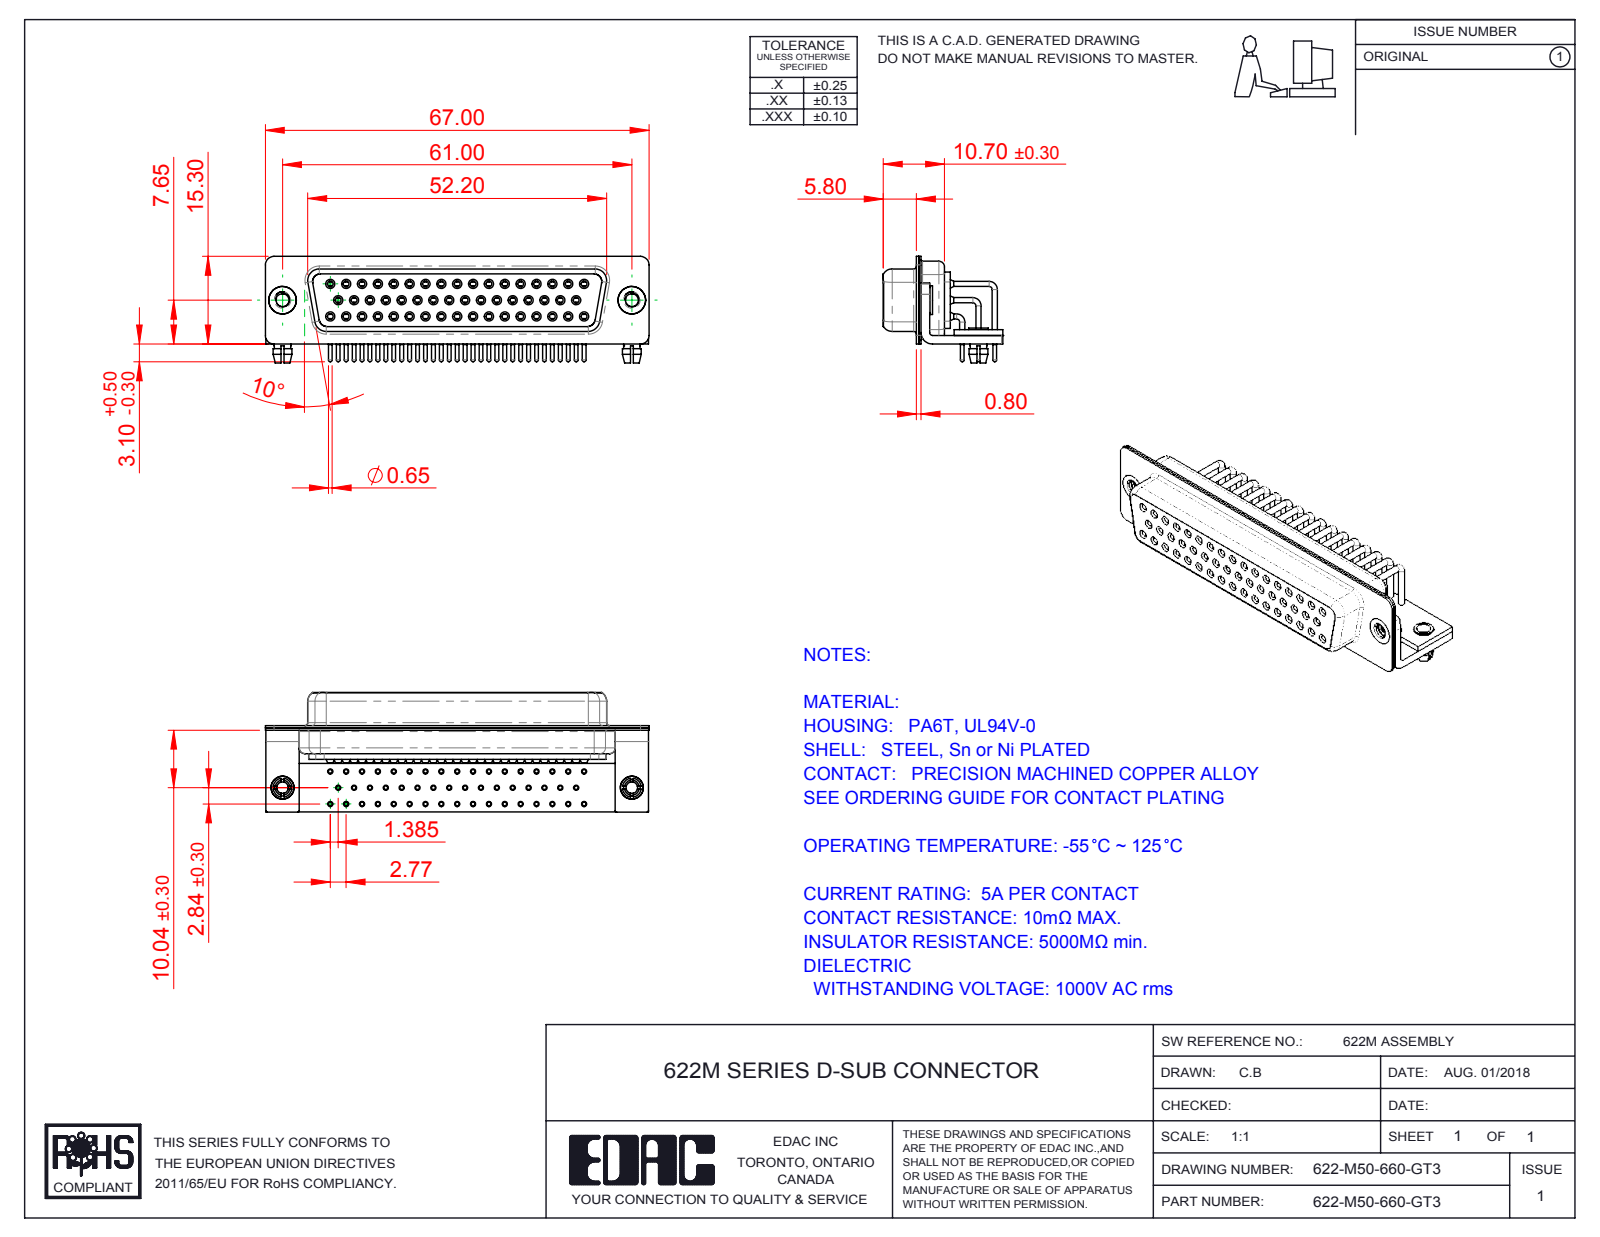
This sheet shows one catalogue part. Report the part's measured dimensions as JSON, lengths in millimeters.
{"part_name": "622M Stabilizer Bracket_50 Contacts; 622M Stabilizer Board_50 Contacts; 622-M50-660-GT3; 622M 4-40 Threaded Rivet_Stabilizer (+7 more)", "step_written_by": "SolidWorks 2016 (CONFIG_CONTROL_DESIGN)", "units": "millimeters", "bodies": {"solids": 60, "faces": 3171, "planar": 891, "cylindrical": 1441, "other": 839}, "overall_size": [67, 20.9, 18.6], "volume_mm3": 7790, "surface_area_mm2": 18357, "round_holes": [[2, 52], [0.9, 50], [1, 50], [1.1, 50], [1.7, 50], [1.8, 50], [2.26, 2], [2.5, 2], [3.2, 2], [4, 2], [4.8, 2]], "round_bosses_or_shafts": [[0.9, 59], [1.6, 50], [1.5, 50], [0.65, 50], [5, 2], [4.9, 2], [4, 2], [3.4, 2]], "partial_cylinders_radius": [[0.25, 16], [1.5, 16], [2, 13], [1.35, 8], [1.6, 8], [0.5, 5], [0.6, 4], [0.65, 4]], "face_to_face_distances": [0.4, 1, 2.2, 0.85, 1.35, 11.85, 12.25, 5.8, 5.9, 0.8], "hole_center_spacings": [2.77, 3.16, 5.54, 8.31, 11.08, 13.85, 16.62, 19.39]}
